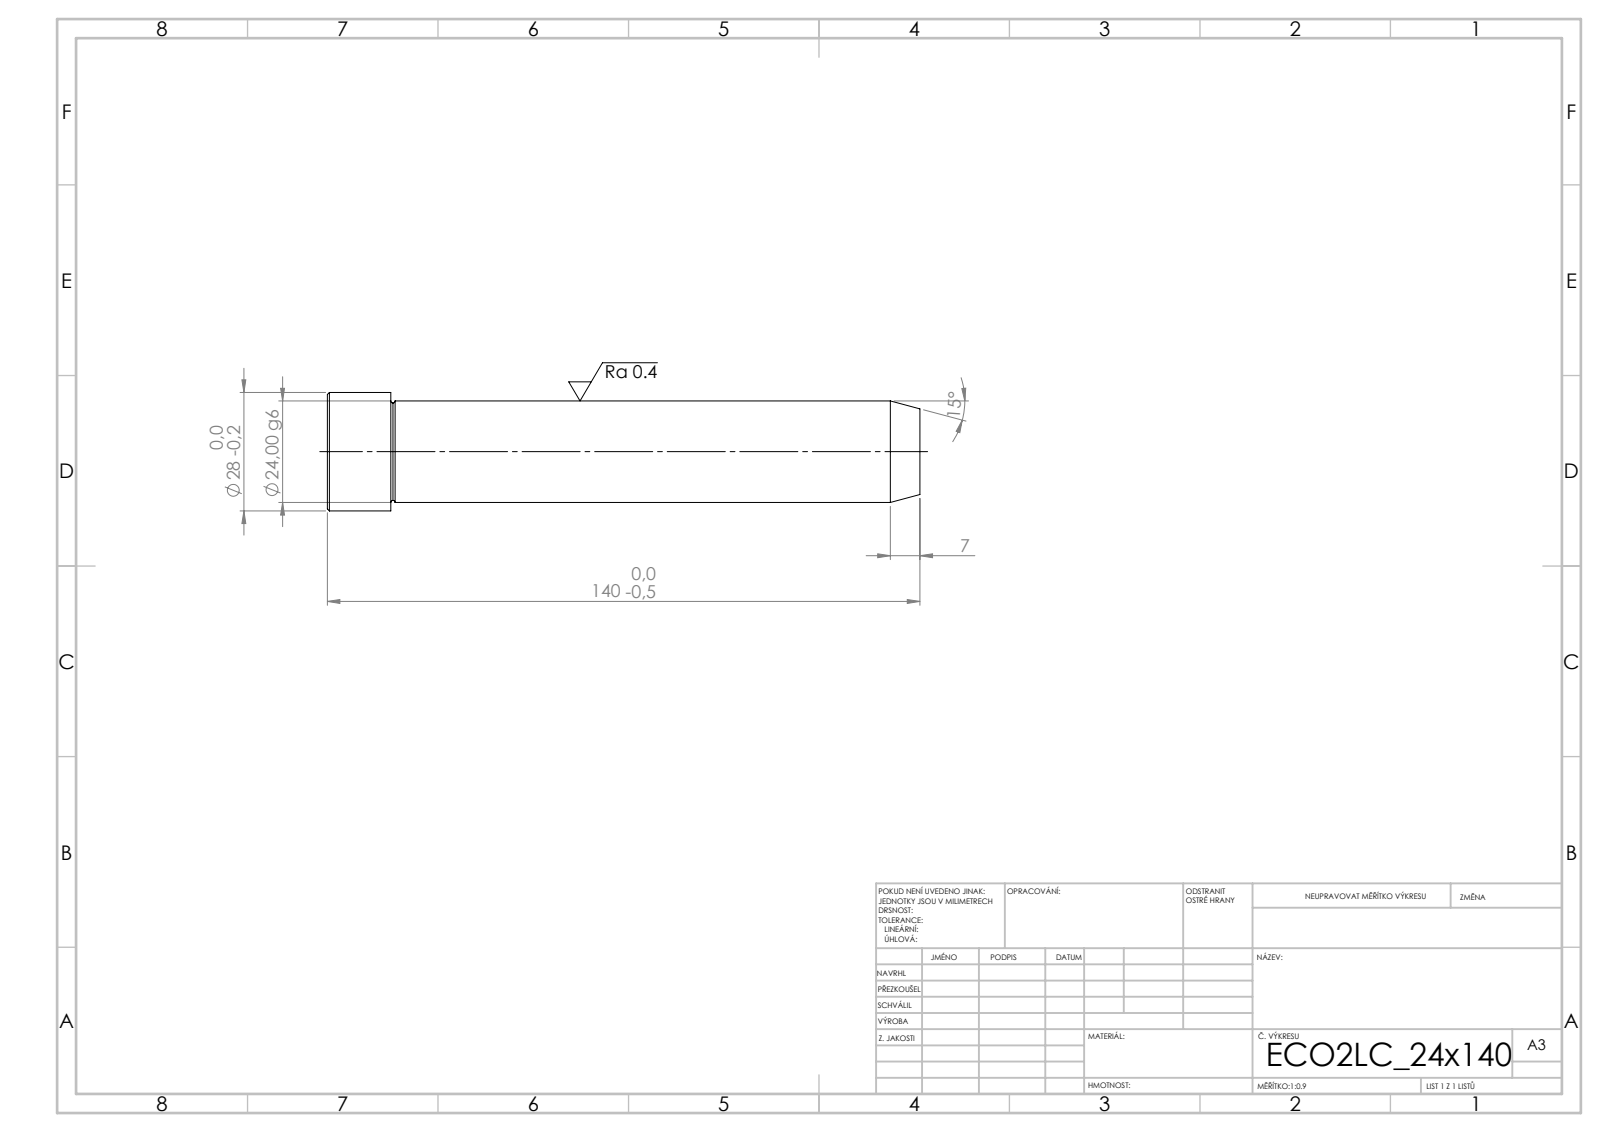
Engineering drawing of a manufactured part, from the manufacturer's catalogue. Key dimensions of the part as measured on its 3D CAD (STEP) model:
STEP written by: SolidWorks 2019 (CONFIG_CONTROL_DESIGN)
Units: millimetres
Bodies: 1 solid, 15 faces (3 planar, 4 cylindrical, 8 other)
Overall size (bounding box): 140 × 28 × 28
Volume: 65 276 mm³ · Surface area: 11 835 mm²
Round bosses / shafts (diameter × count): ⌀28 ×1, ⌀24 ×1
Main face-to-face distances: 140, 125, 15
